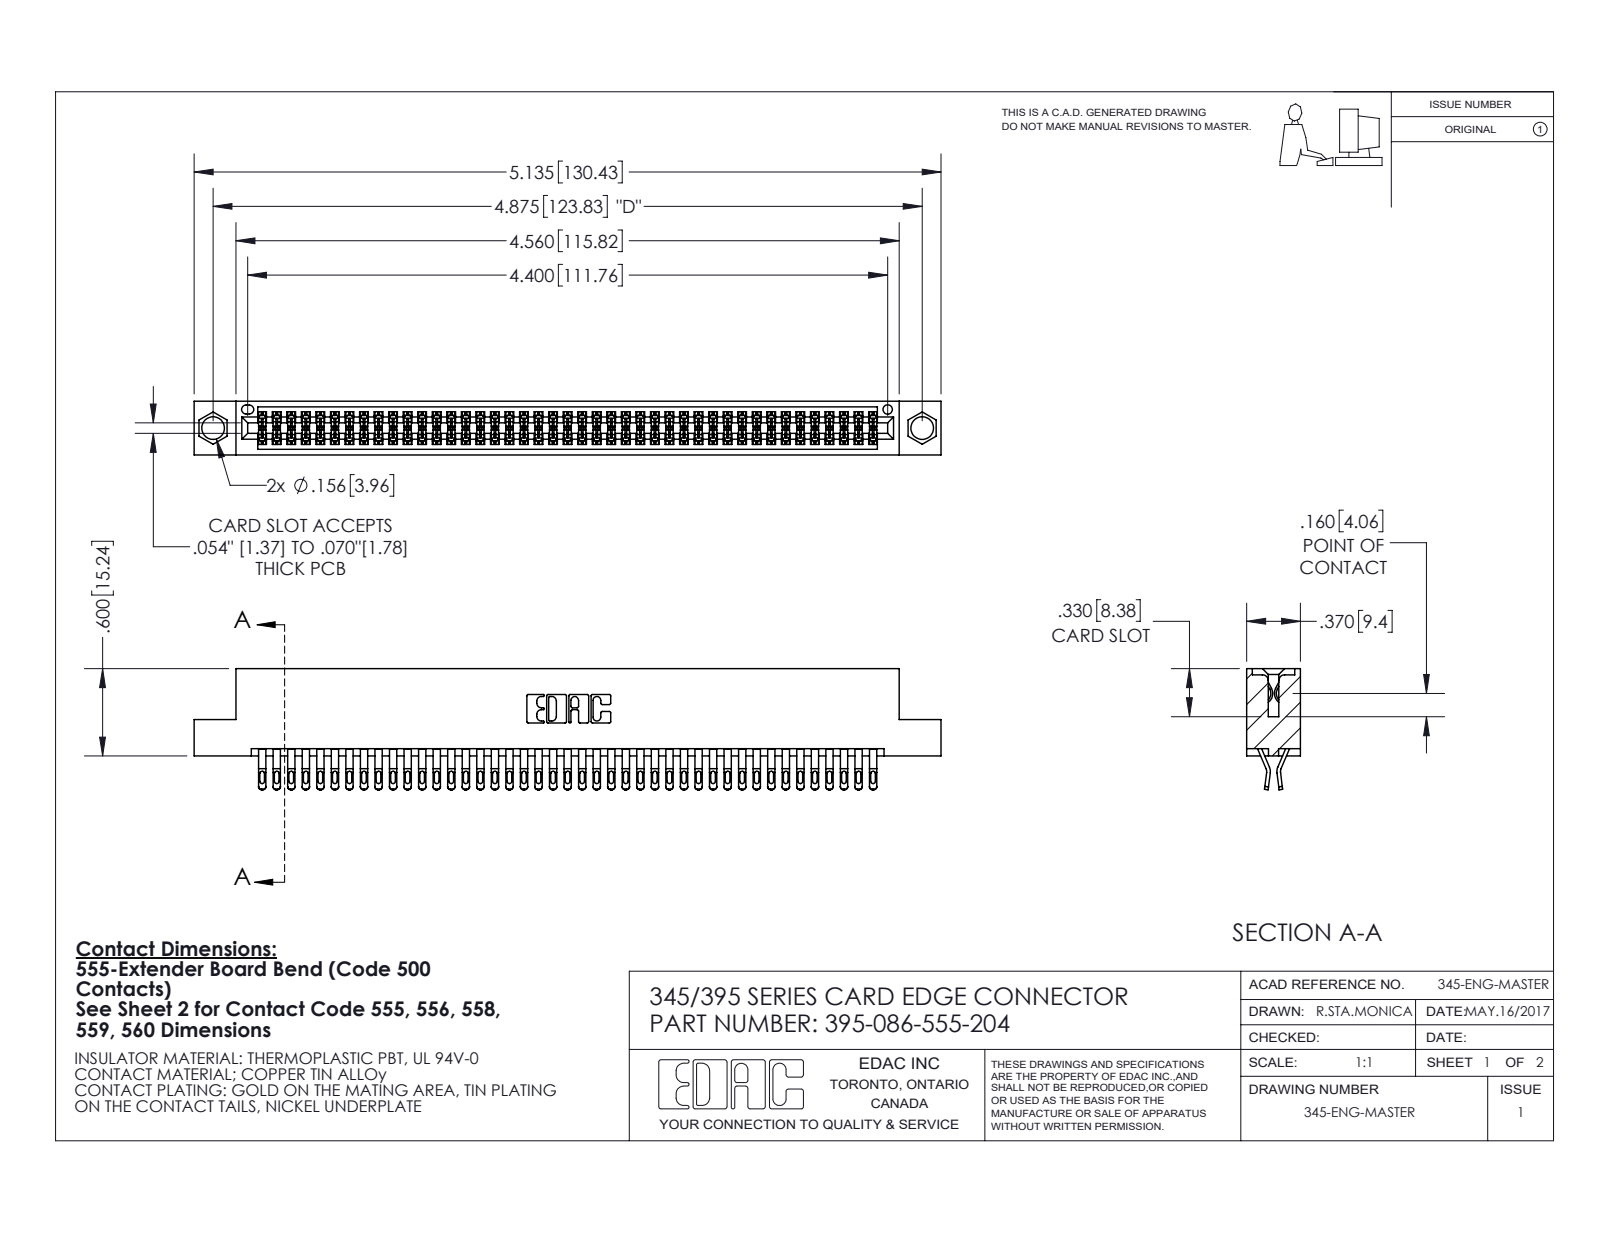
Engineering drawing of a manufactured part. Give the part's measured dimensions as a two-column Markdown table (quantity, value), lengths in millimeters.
| quantity | value |
| --- | --- |
| part name | 395-086-555-204; 345-292-001_555 Tail; 345 Part_Flush Mounting Lugs - 0.156 Dia-TI |
| STEP written by | SolidWorks 2020 (CONFIG_CONTROL_DESIGN) |
| units | millimeters |
| bodies | 87 solids, 4956 faces (2760 planar, 2196 cylindrical, 0 other) |
| overall size | 130.4 × 21.1 × 9.4 |
| volume | 12 800 mm³ |
| surface area | 19 690 mm² |
| round holes (diameter × count) | 4 × 2, 1.6 × 1 |
| partial cylindrical surfaces (radius × count) | 0.4 × 215, 0.2 × 172, 0.5 × 172, 0.3 × 22, 0.2 × 6, 0.8 × 6, 0.7 × 3, 0.3 × 2 |
| main face-to-face distances | 7.6, 1.8, 0.6, 9.4, 5.1, 2.5, 6.9, 5.7, 4.4, 3.8 |
| hole center spacings | 6.9, 117.8, 123.8 |
